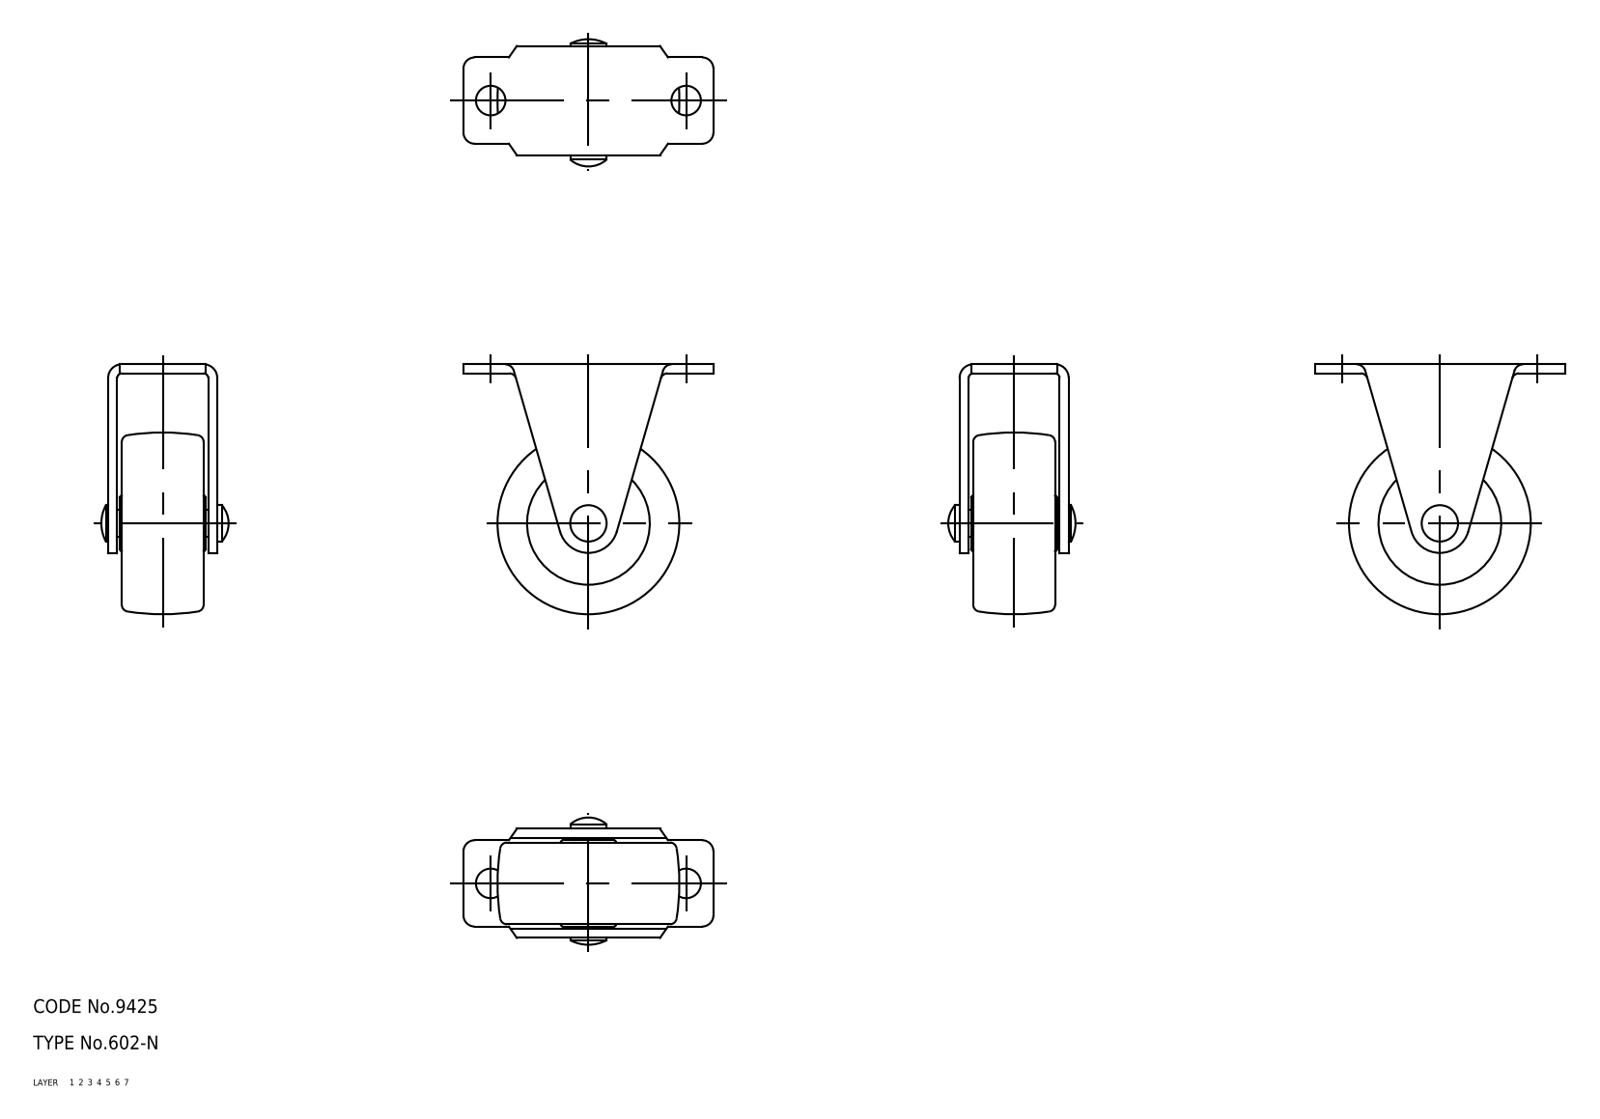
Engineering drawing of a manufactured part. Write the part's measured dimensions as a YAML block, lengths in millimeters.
part_name: "wheel; axle; No_602_N_13957_36"
step_written_by: "CADfix (AUTOMOTIVE_DESIGN)"
units: millimeters
bodies: {solids: 3, faces: 106, planar: 0, cylindrical: 0, other: 106}
overall_size: [55, 55, 28]
volume: 22548
surface_area: 12654
